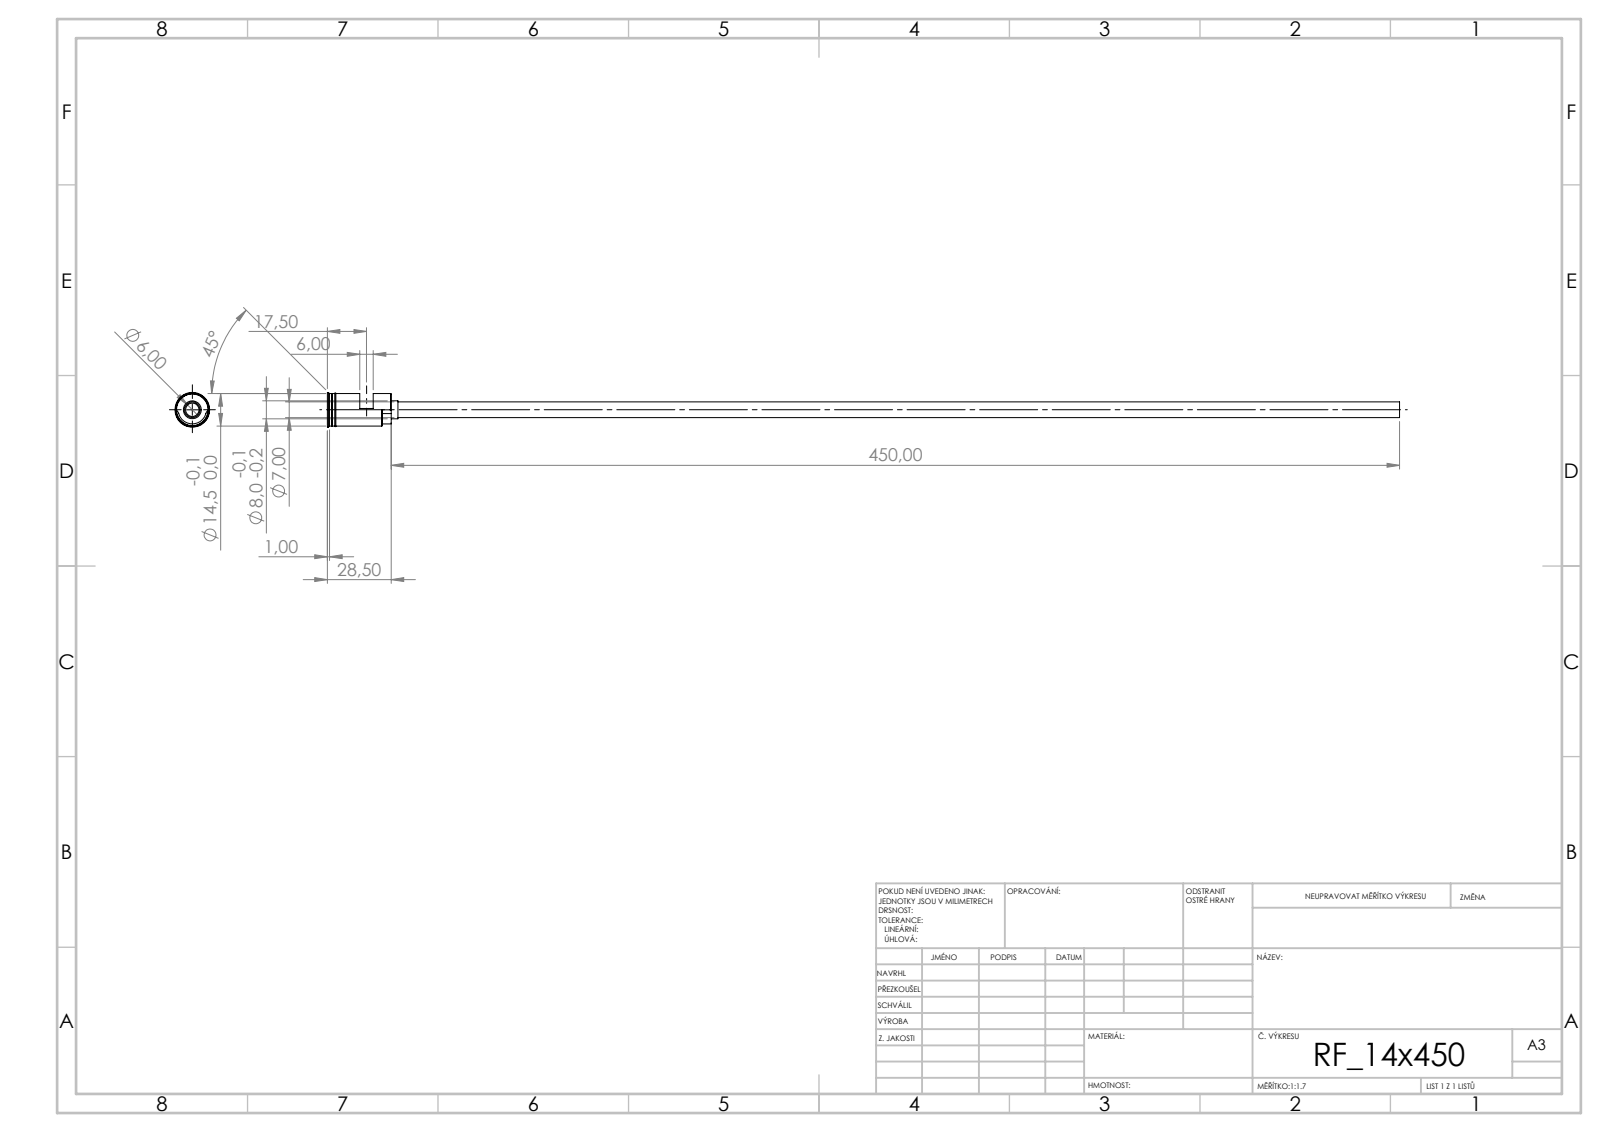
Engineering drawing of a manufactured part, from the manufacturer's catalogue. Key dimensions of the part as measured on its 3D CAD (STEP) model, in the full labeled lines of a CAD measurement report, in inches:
STEP written by: SolidWorks 2019 (CONFIG_CONTROL_DESIGN)
Units: inches
Bodies: 1 solid, 55 faces (24 planar, 19 cylindrical, 12 other)
Overall size (bounding box): 18.839 × 0.61 × 0.61
Volume: 0.509 in³ · Surface area: 31.6 in²
Round holes (diameter × count): ⌀0.236 ×1
Round bosses / shafts (diameter × count): ⌀0.61 ×1, ⌀0.571 ×1, ⌀0.563 ×1, ⌀0.315 ×1, ⌀0.276 ×1
Partial cylindrical surfaces — rounded edges, fillets, slot ends (radius × count): R0.118 ×2, R0.248 ×1
Main face-to-face distances: 0.571, 0.551, 1.122, 1.043, 0.492, 0.079, 0.315, 0.236, 0.728, 0.807
